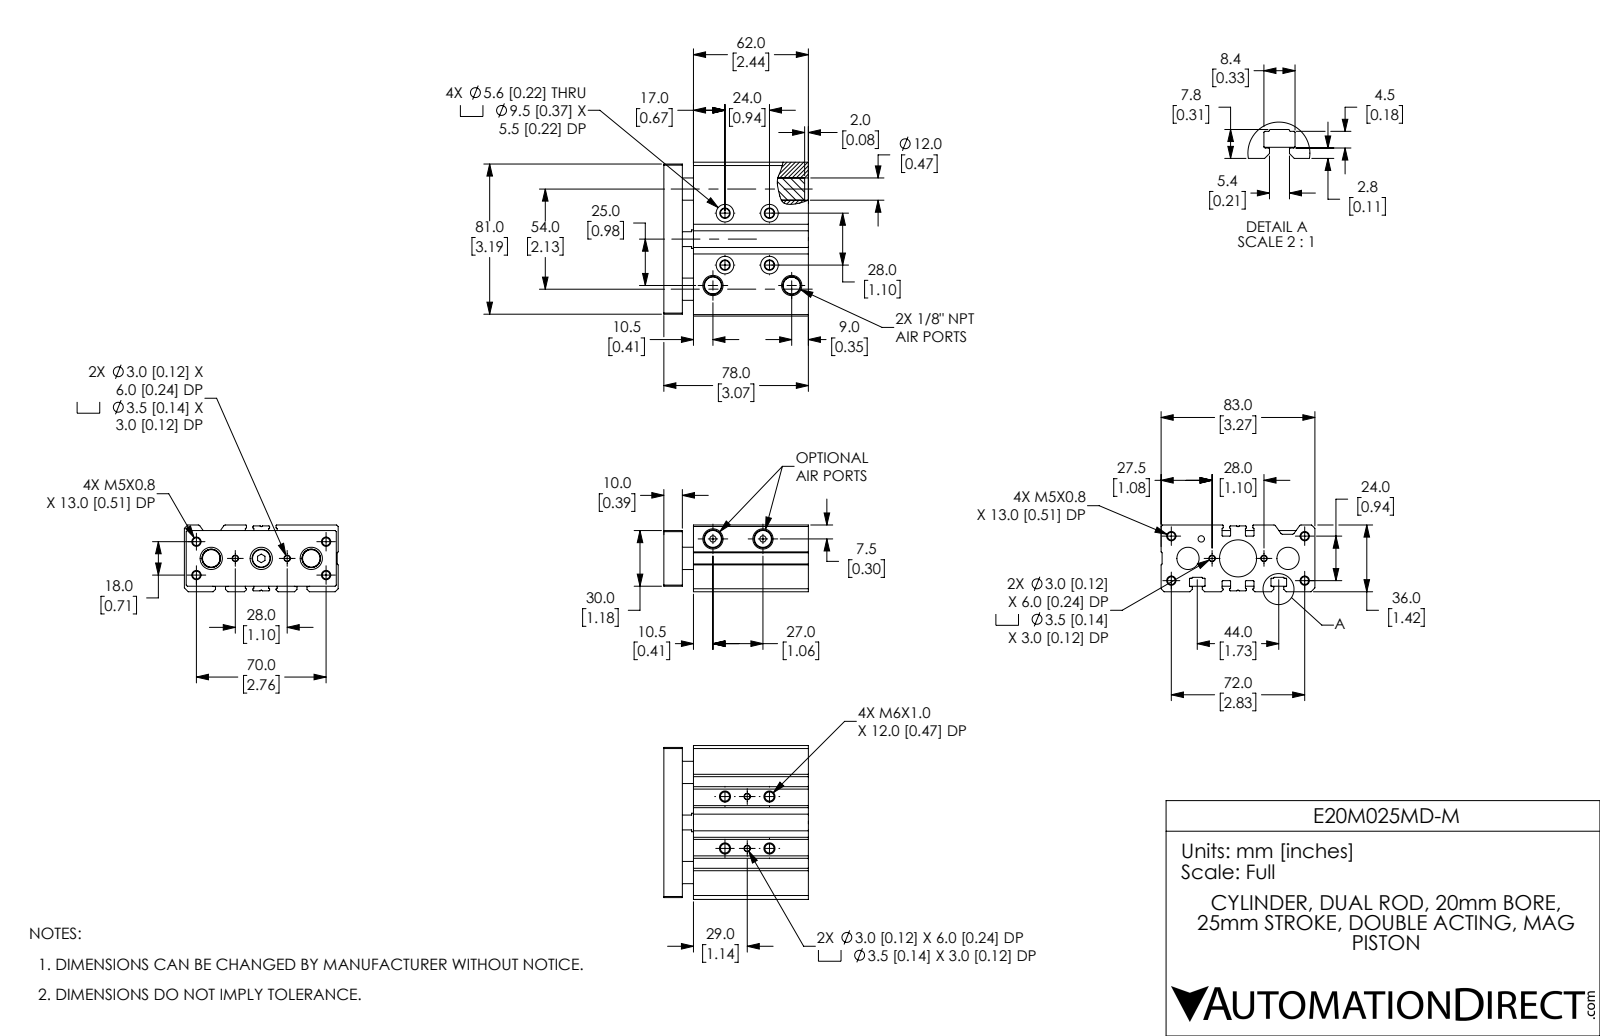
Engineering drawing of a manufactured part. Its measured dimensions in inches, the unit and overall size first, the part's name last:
Units: inches
Overall size (bounding box): 3.268 × 3.071 × 1.417
Round holes (diameter × count): ⌀0.163 ×8, ⌀0.118 ×4, ⌀0.138 ×4, ⌀0.194 ×4, ⌀0.22 ×4, ⌀0.374 ×4, ⌀0.236 ×3, ⌀0.472 ×3, ⌀0.135 ×2, ⌀0.39 ×2, ⌀0.135 ×1, ⌀0.472 ×1
Round bosses / shafts (diameter × count): ⌀0.394 ×1, ⌀0.39 ×1
Partial cylindrical surfaces — rounded edges, fillets, slot ends (radius × count): R0.016 ×20, R0.008 ×18, R0.012 ×10, R0.01 ×8, R0.039 ×4
Main face-to-face distances: 0.236, 0.118, 1.417, 0.63, 2.677, 0.02, 3.071, 2.441, 0.394, 1.181
Hole centre spacings: 0.124, 0.472, 0.474, 0.591, 0.828, 0.9, 0.945, 0.987
Volume: 10.82 in³ · Surface area: 88.6 in²
Bodies: 5 solids, 404 faces (128 planar, 182 cylindrical, 94 other)
Part name (STEP PRODUCT): E20M025MD-M; E20M025MD-M_BODY; E20M025MD-M_ENDPLATE
STEP written by: SolidWorks 2019 (CONFIG_CONTROL_DESIGN)
